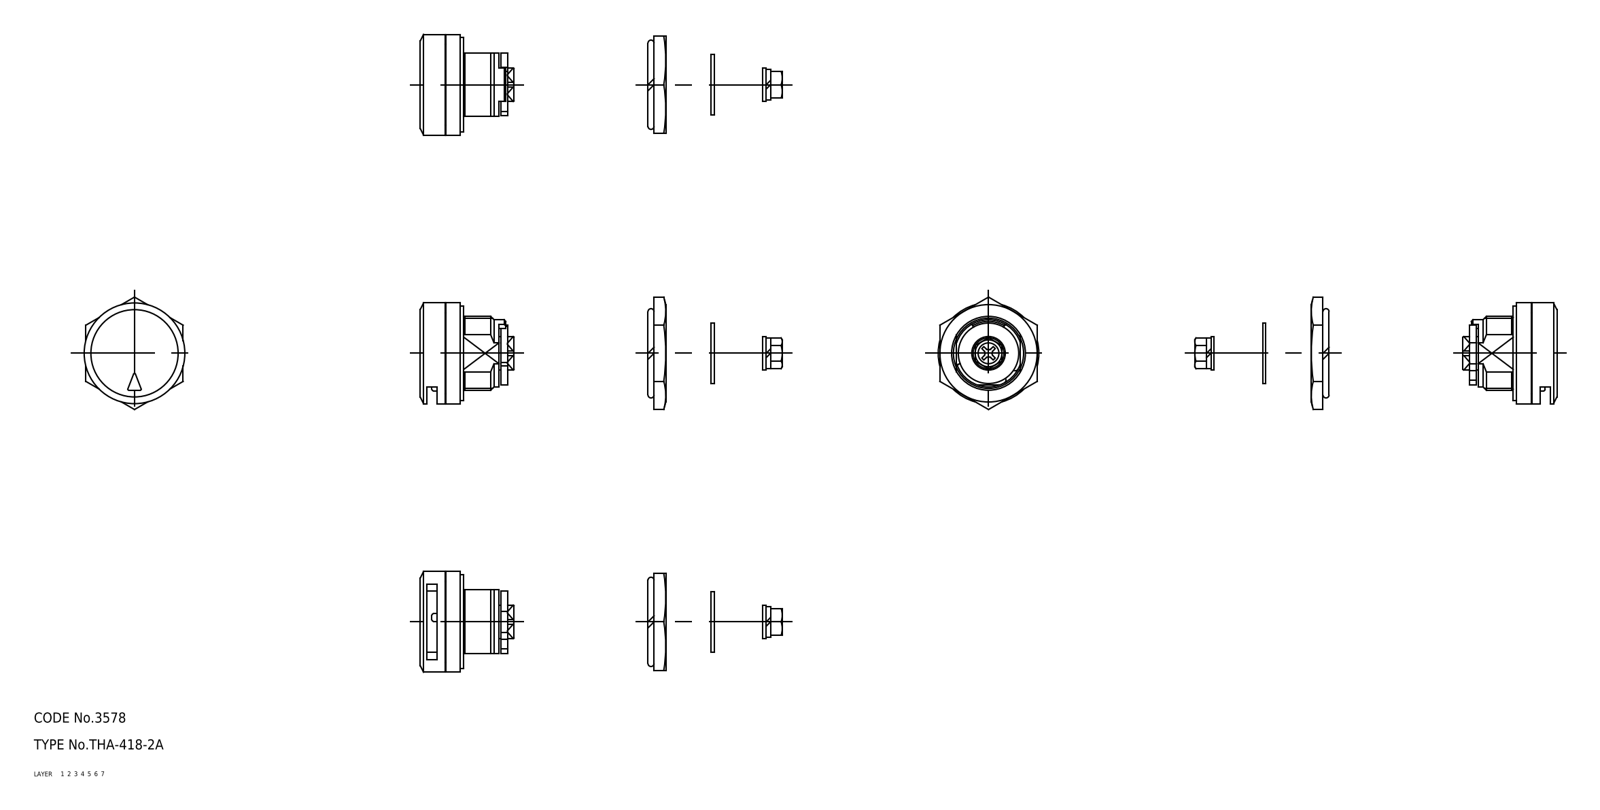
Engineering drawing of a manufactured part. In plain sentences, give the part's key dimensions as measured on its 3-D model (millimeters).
The part is named "washer; rotor; packing; nut (+3 more)". Its 3-D file was written by "CADfix (AUTOMOTIVE_DESIGN)". It is 7 solids with 214 faces: 0 planar, 0 cylindrical and 214 other. Overall it measures 33.8 by 33.49 by 30 millimeters. Its volume is 13 183 cubic millimeters and its surface area 11 097 square millimeters.
